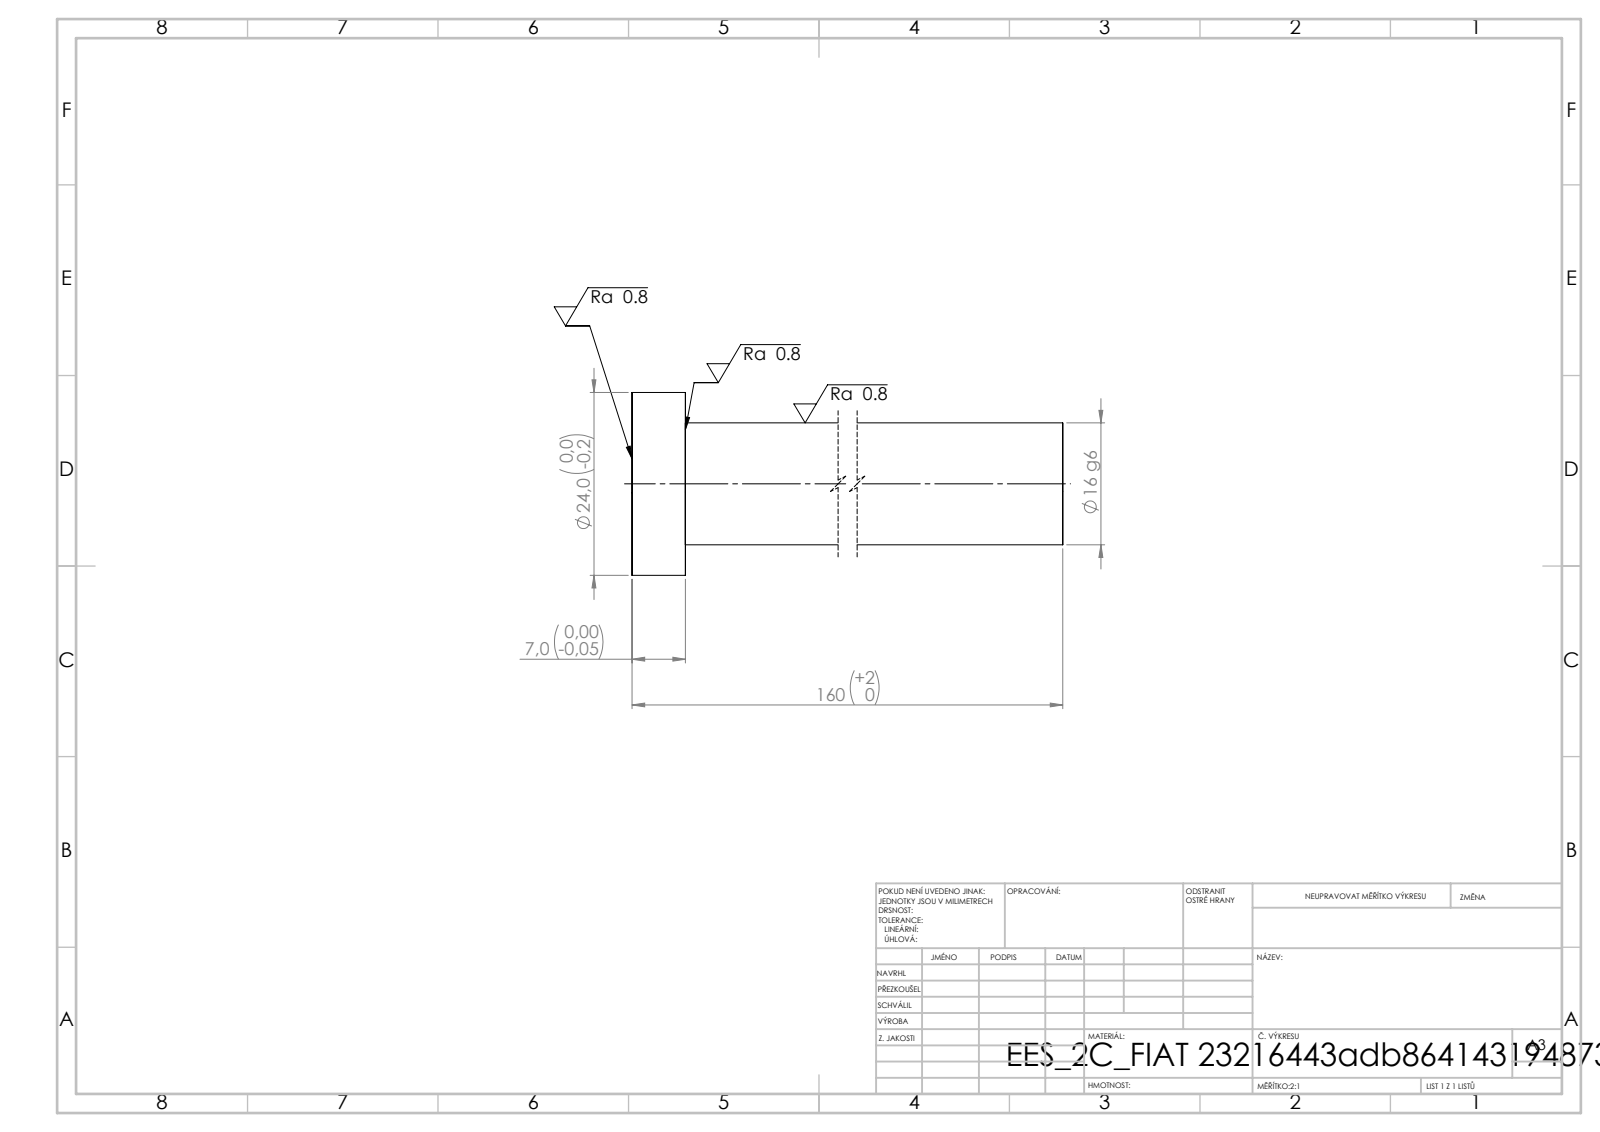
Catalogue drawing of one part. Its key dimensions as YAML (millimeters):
step_written_by: "SolidWorks 2019 (CONFIG_CONTROL_DESIGN)"
units: millimeters
bodies: {solids: 1, faces: 7, planar: 3, cylindrical: 4, other: 0}
overall_size: [160, 24, 24]
volume: 33929
surface_area: 9123
round_bosses_or_shafts:
  - {diameter: 24, count: 1}
  - {diameter: 16, count: 1}
face_to_face_distances: [7, 160, 153]
